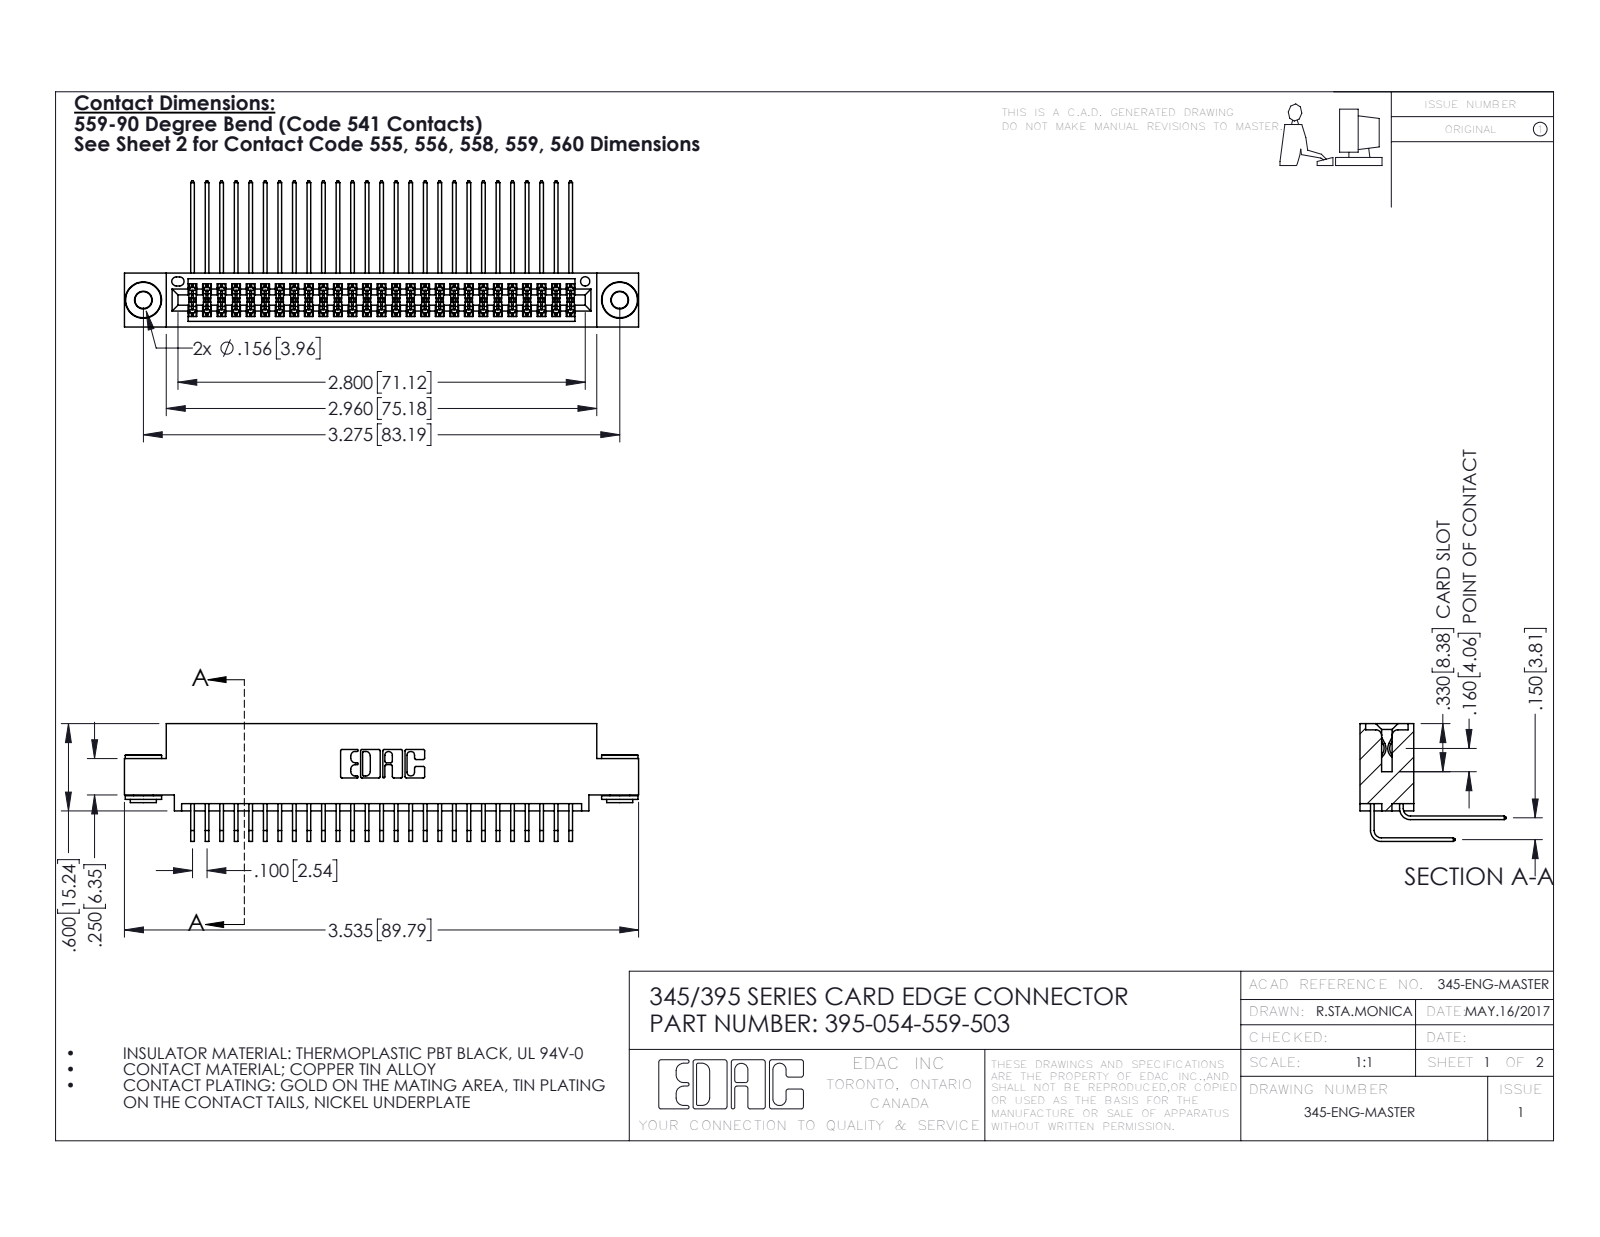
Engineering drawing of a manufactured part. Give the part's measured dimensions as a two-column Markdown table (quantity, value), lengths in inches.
| quantity | value |
| --- | --- |
| part name | 395-054-559-503; 345 Part_0.110 Offset - 0.156 Dia-TH; 345-292-001_559 Tail - 2; 345-292-001_558 559 Tail - 1 (+1 more) |
| STEP written by | SolidWorks 2016 (CONFIG_CONTROL_DESIGN) |
| units | inches |
| bodies | 57 solids, 2976 faces (1984 planar, 984 cylindrical, 8 other) |
| overall size | 3.535 × 1.005 × 0.809 |
| volume | 0.539 in³ |
| surface area | 22.54 in² |
| round holes (diameter × count) | 0.116 × 2, 0.156 × 2, 0.064 × 1 |
| round bosses / shafts (diameter × count) | 0.25 × 2, 0.18 × 2, 0.136 × 2 |
| partial cylindrical surfaces (radius × count) | 0.006 × 81, 0.01 × 22, 0.007 × 6, 0.031 × 6, 0.026 × 3, 0.014 × 2, 0.019 × 2, 0.022 × 2 |
| main face-to-face distances | 0.072, 0.298, 0.2, 0.37, 0.025, 0.098, 0.272, 0.225, 0.15, 0.175 |
| hole center spacings | 0.27, 3.04, 3.275 |
